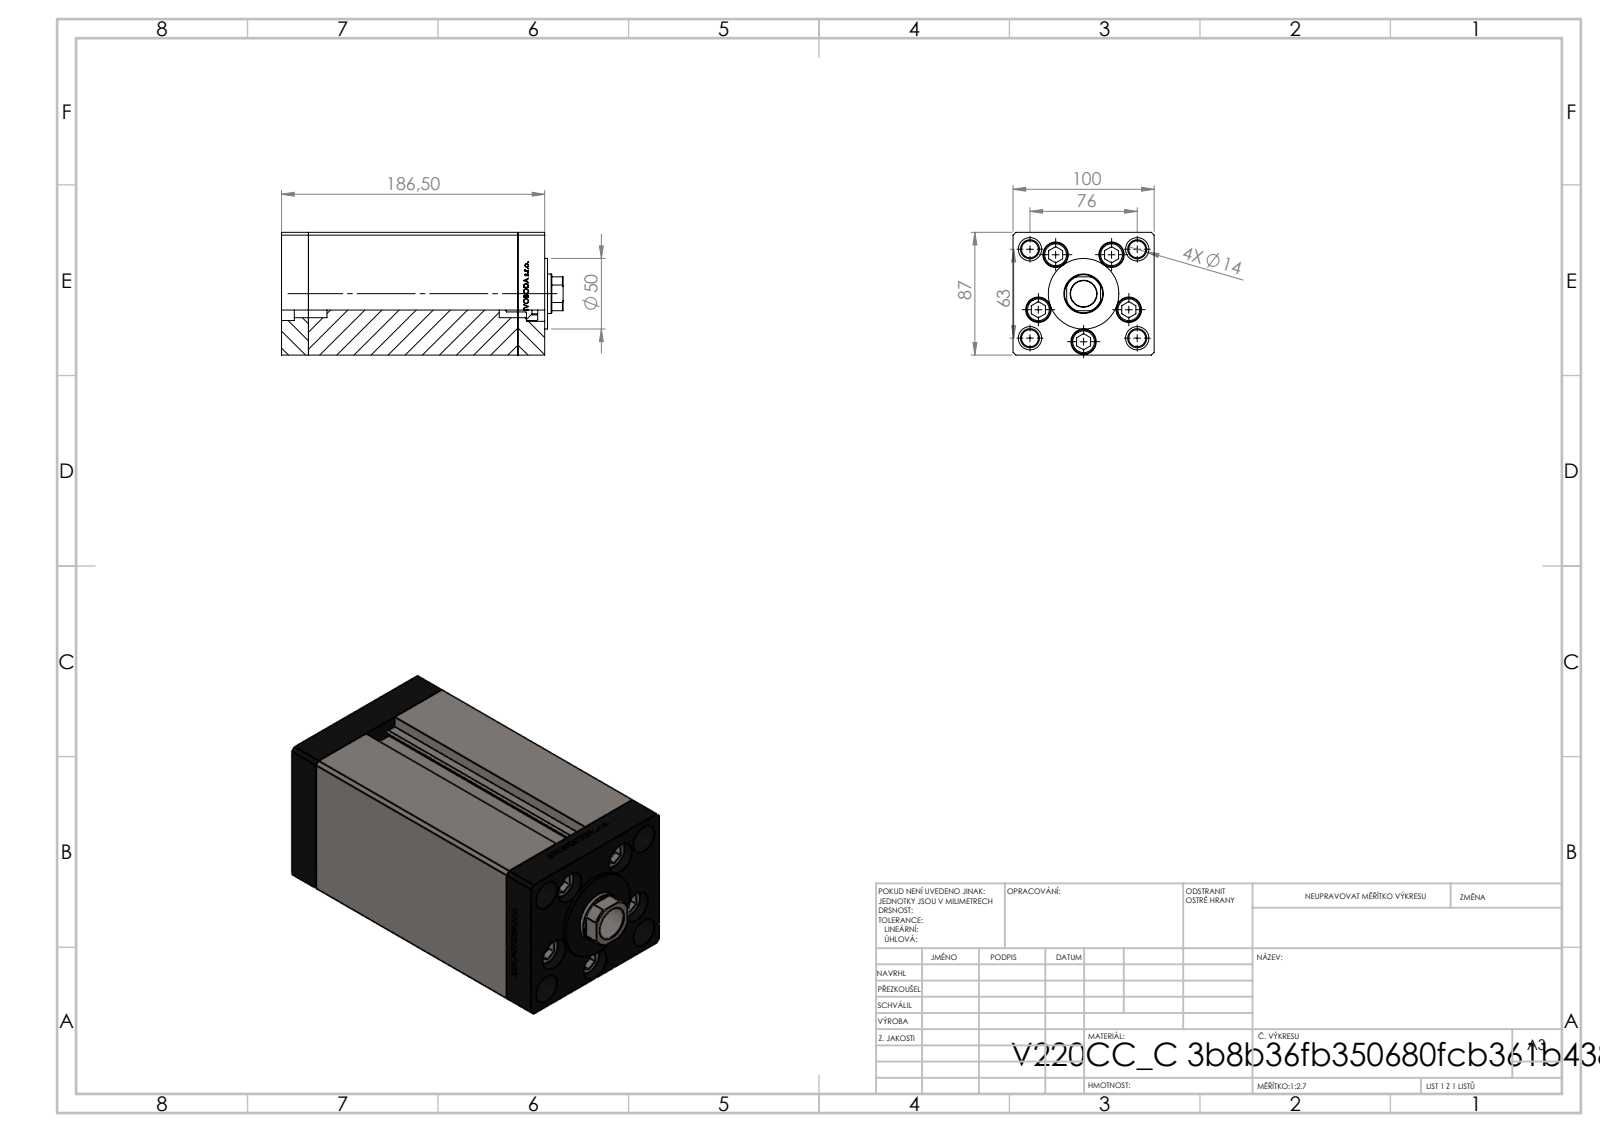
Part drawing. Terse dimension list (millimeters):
name: V220C FRONT; ALLEN BOLT; V220C_VC_C; V220C BACK_C (+1 more)
written by: SolidWorks 2019 (CONFIG_CONTROL_DESIGN)
unit: mm
bodies: 13 solids, 1160 faces (538 planar, 160 cylindrical, 462 other)
size: 199.5 × 100 × 87
volume: 1 335 000 mm³; area: 228 555 mm²
holes: 9× ⌀13.5, 5× ⌀18, 4× ⌀12, 4× ⌀16.5, 1× ⌀17, 1× ⌀18.5, 1× ⌀28
bosses: 5× ⌀8, 4× ⌀17, 1× ⌀50
rounds: 2× R0.93, 1× R13.5
face distances: 100, 87, 19, 148.5, 167.5, 34.25, 186.5, 152.25, 133.25, 15.25
hole spacings: 34, 49.36, 18.59, 21.03, 38.08, 39.27, 40.83, 43.24
